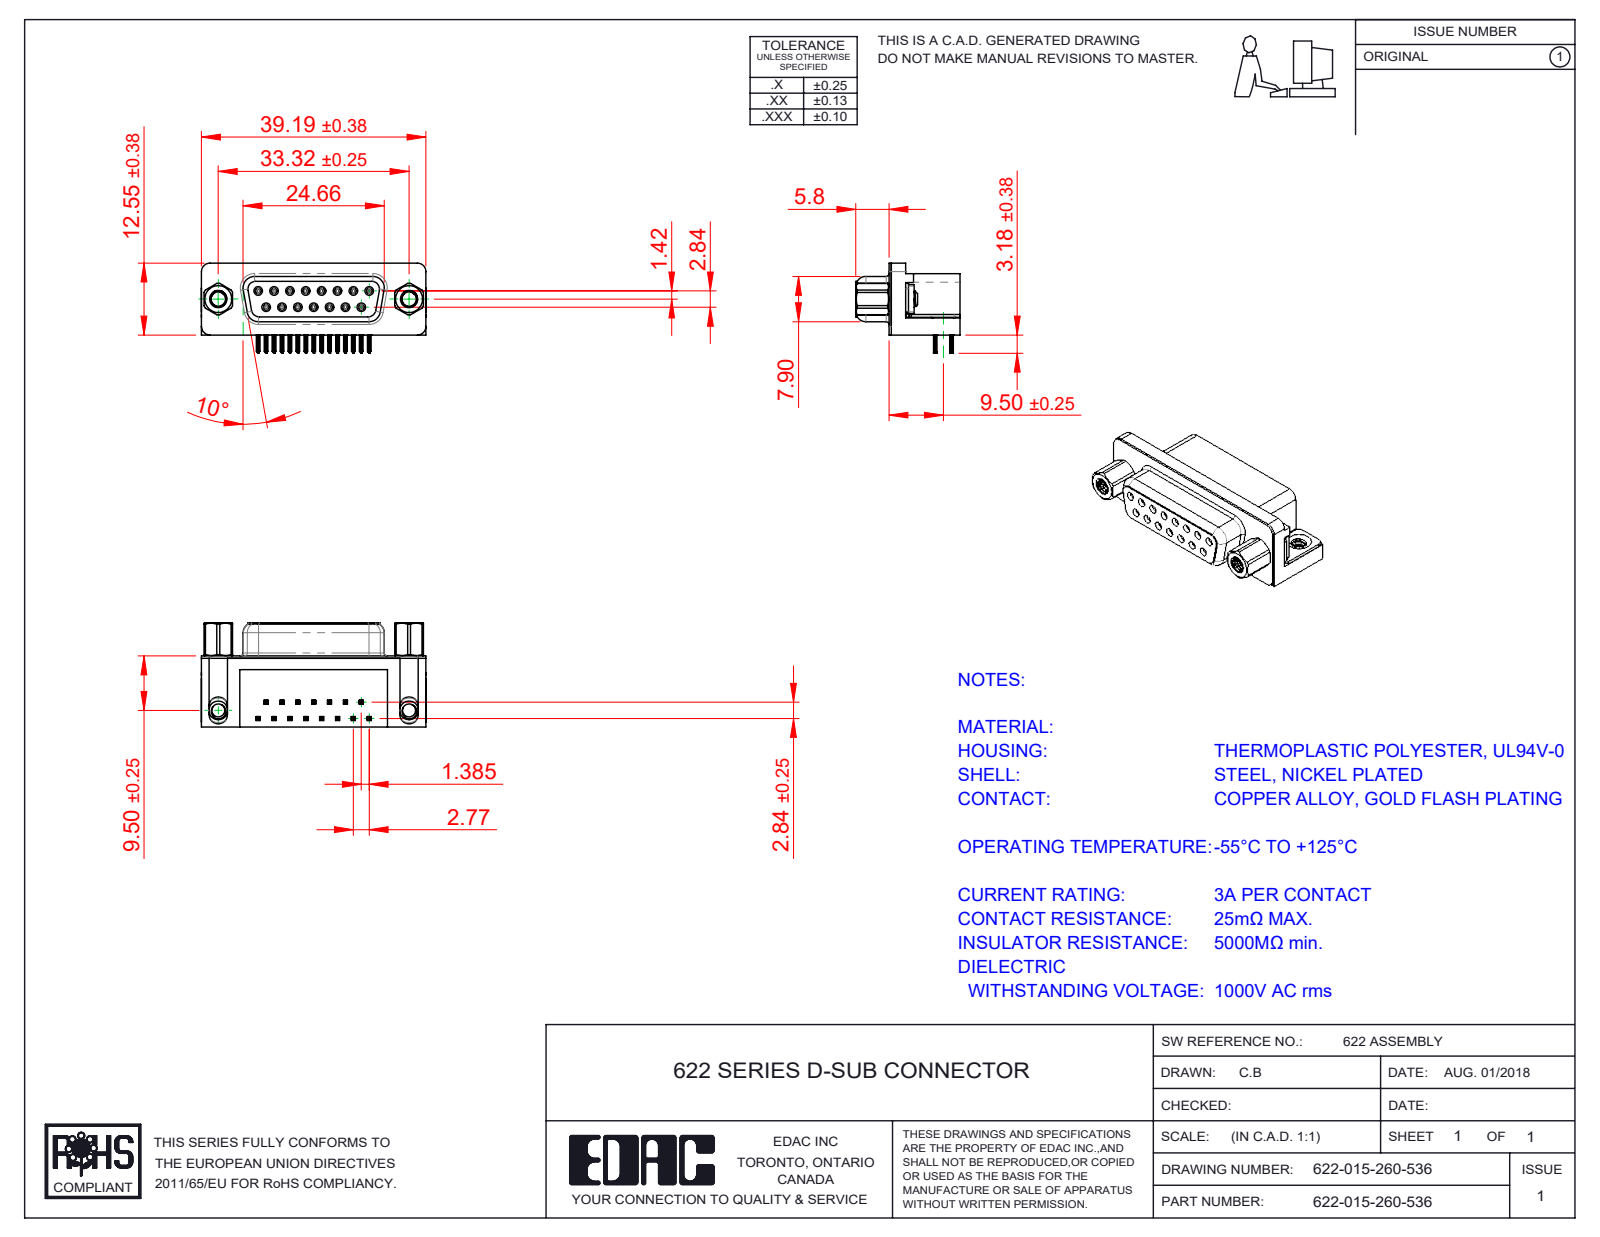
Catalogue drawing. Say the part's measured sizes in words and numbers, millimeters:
The part is named "622 2 Prong Board Lock; 622-015-260-536; 622 M3 Threaded Rivet; 622 Contact Top (+3 more)". Its 3-D file was written by "SolidWorks 2016 (CONFIG_CONTROL_DESIGN)". It is 21 solids with 2467 faces: 1106 planar, 617 cylindrical and 744 other. Overall it measures 39.22 by 18.2 by 16.25 millimeters. Its volume is 5 182 cubic millimeters and its surface area 6 725 square millimeters. Round holes: 15 of diameter 0.8, 15 of diameter 0.9, 2 of diameter 2.5, 2 of diameter 4, 2 of diameter 4.8, 2 of diameter 5. Round bosses or shafts: 15 of diameter 1.2, 2 of diameter 4.9, 2 of diameter 4.75, 2 of diameter 3.9. Partial cylindrical surfaces (rounded edges, fillets, slot ends): 120 of radius 0.1, 60 of radius 0.15, 30 of radius 0.35, 18 of radius 1, 15 of radius 0.34, 10 of radius 0.5, 8 of radius 0.25, 8 of radius 1.35. The main face-to-face distances are 0.4, 12, 6.2, 12.4, 10.35, 2.9, 0.85, 6.65, 0.35, 0.5. The hole center spacings are 3.16, 2.77, 5.54, 8.31, 11.08, 5.03, 5.04, 7.48.
